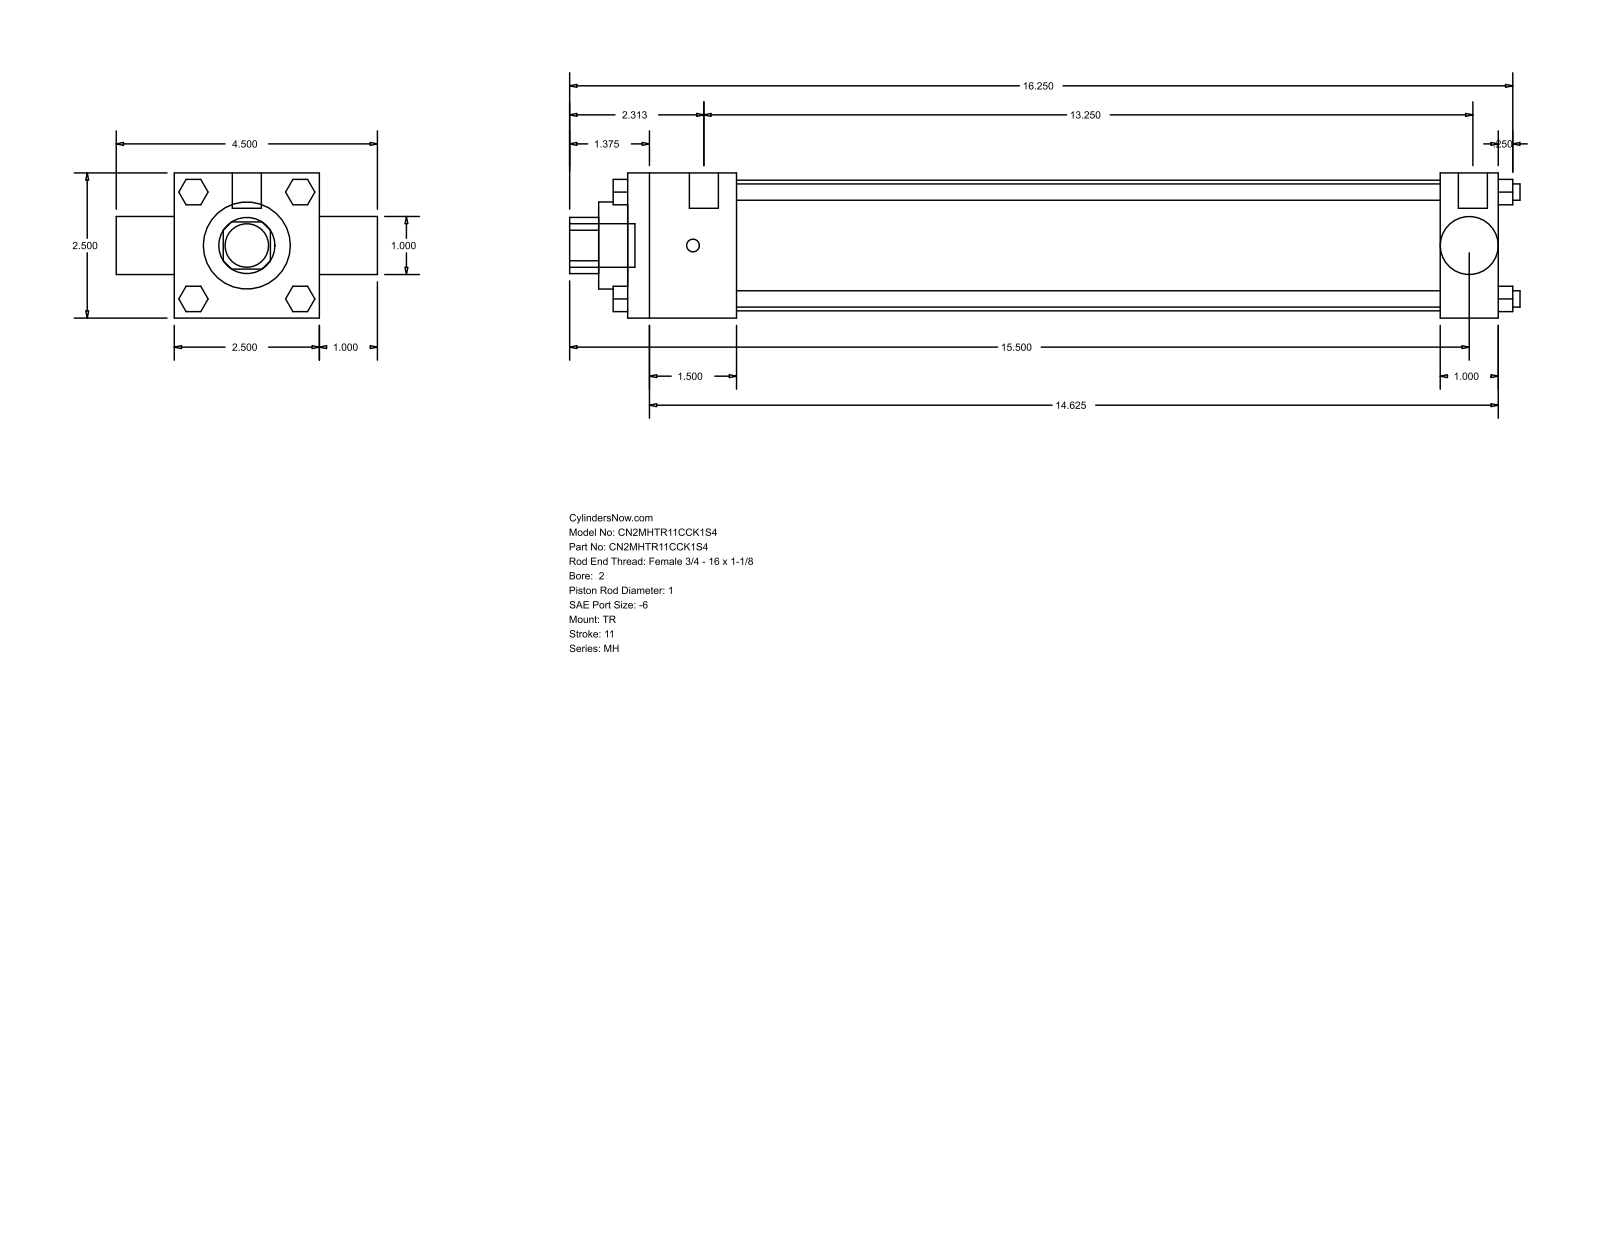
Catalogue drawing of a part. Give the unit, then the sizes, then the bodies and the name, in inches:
Units: inches
Overall size (bounding box): 16.375 × 4.5 × 2.5
Round holes (diameter × count): ⌀0.998 ×1, ⌀1 ×1, ⌀1.5 ×1, ⌀2.25 ×1
Round bosses / shafts (diameter × count): ⌀0.281 ×4, ⌀0.219 ×3, ⌀0.5 ×2, ⌀0.75 ×1
Partial cylindrical surfaces — rounded edges, fillets, slot ends (radius × count): R0.484 ×1
Main face-to-face distances: 2.5, 15, 1, 1.875, 14, 12.125, 13.125, 3.5, 15.5, 0.25
Bodies: 0 solids, 120 faces (92 planar, 28 cylindrical, 0 other)
Part name (STEP PRODUCT): MH_TR__0200_1
STEP written by: GSSL Pune (CONFIG_CONTROL_DESIGN)
